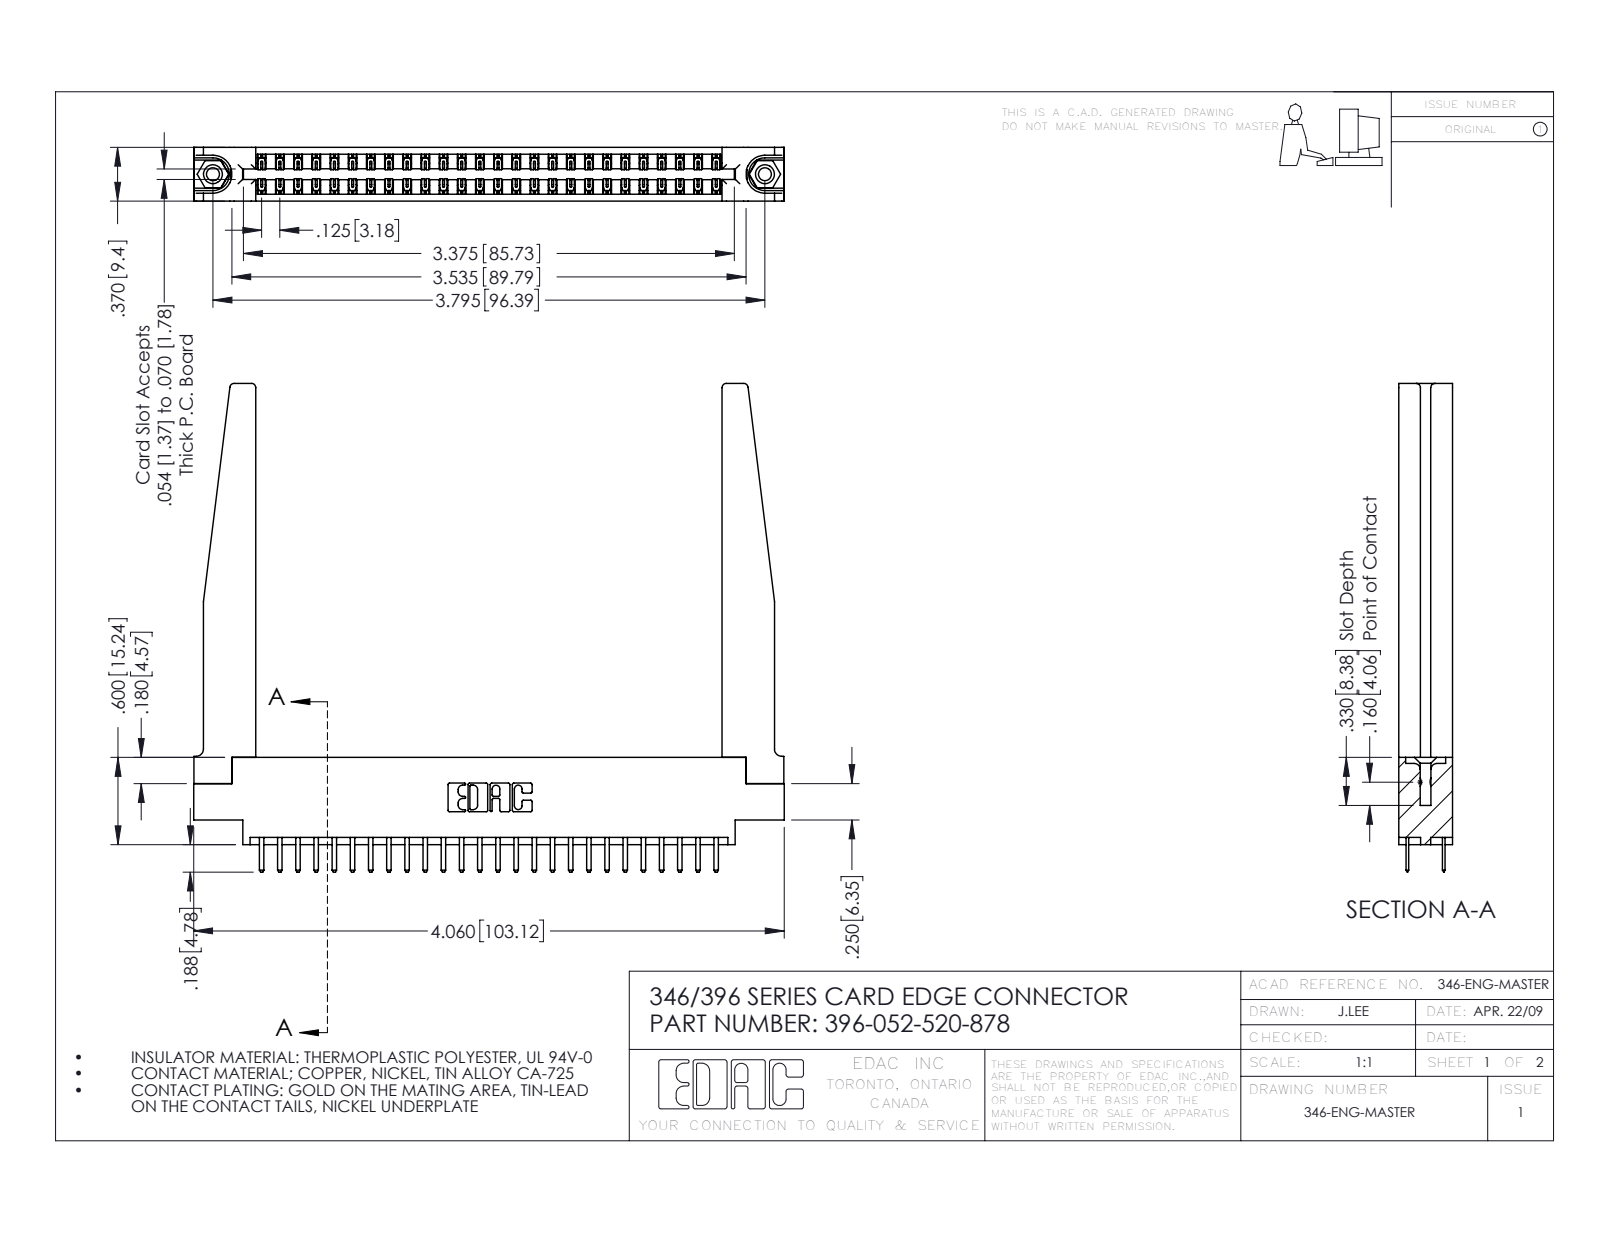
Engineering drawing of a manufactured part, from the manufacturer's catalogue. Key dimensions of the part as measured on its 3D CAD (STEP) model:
Part name (STEP PRODUCT): 396-052-520-878; 346-220-078_345-220-078; 346 Part_0.170 Offset - 0.156 Dia-TH; 345-292-001_345-293-120 (+1 more)
STEP written by: SolidWorks 2016 (CONFIG_CONTROL_DESIGN)
Units: inches
Bodies: 57 solids, 3272 faces (2146 planar, 1074 cylindrical, 52 other)
Overall size (bounding box): 4.06 × 3.358 × 0.37
Volume: 1.017 in³ · Surface area: 30.72 in²
Round holes (diameter × count): ⌀0.089 ×2, ⌀0.125 ×2, ⌀0.156 ×2, ⌀0.064 ×1
Round bosses / shafts (diameter × count): ⌀0.155 ×2
Partial cylindrical surfaces — rounded edges, fillets, slot ends (radius × count): R0.006 ×78, R0.01 ×56, R0.01 ×22, R0.03 ×8, R0.007 ×6, R0.031 ×6, R0.026 ×3, R0.014 ×2
Main face-to-face distances: 0.37, 0.048, 0.322, 0.072, 0.148, 0.15, 0.25, 0.298, 0.025, 0.275
Hole centre spacings: 0.246, 3.587, 3.795
